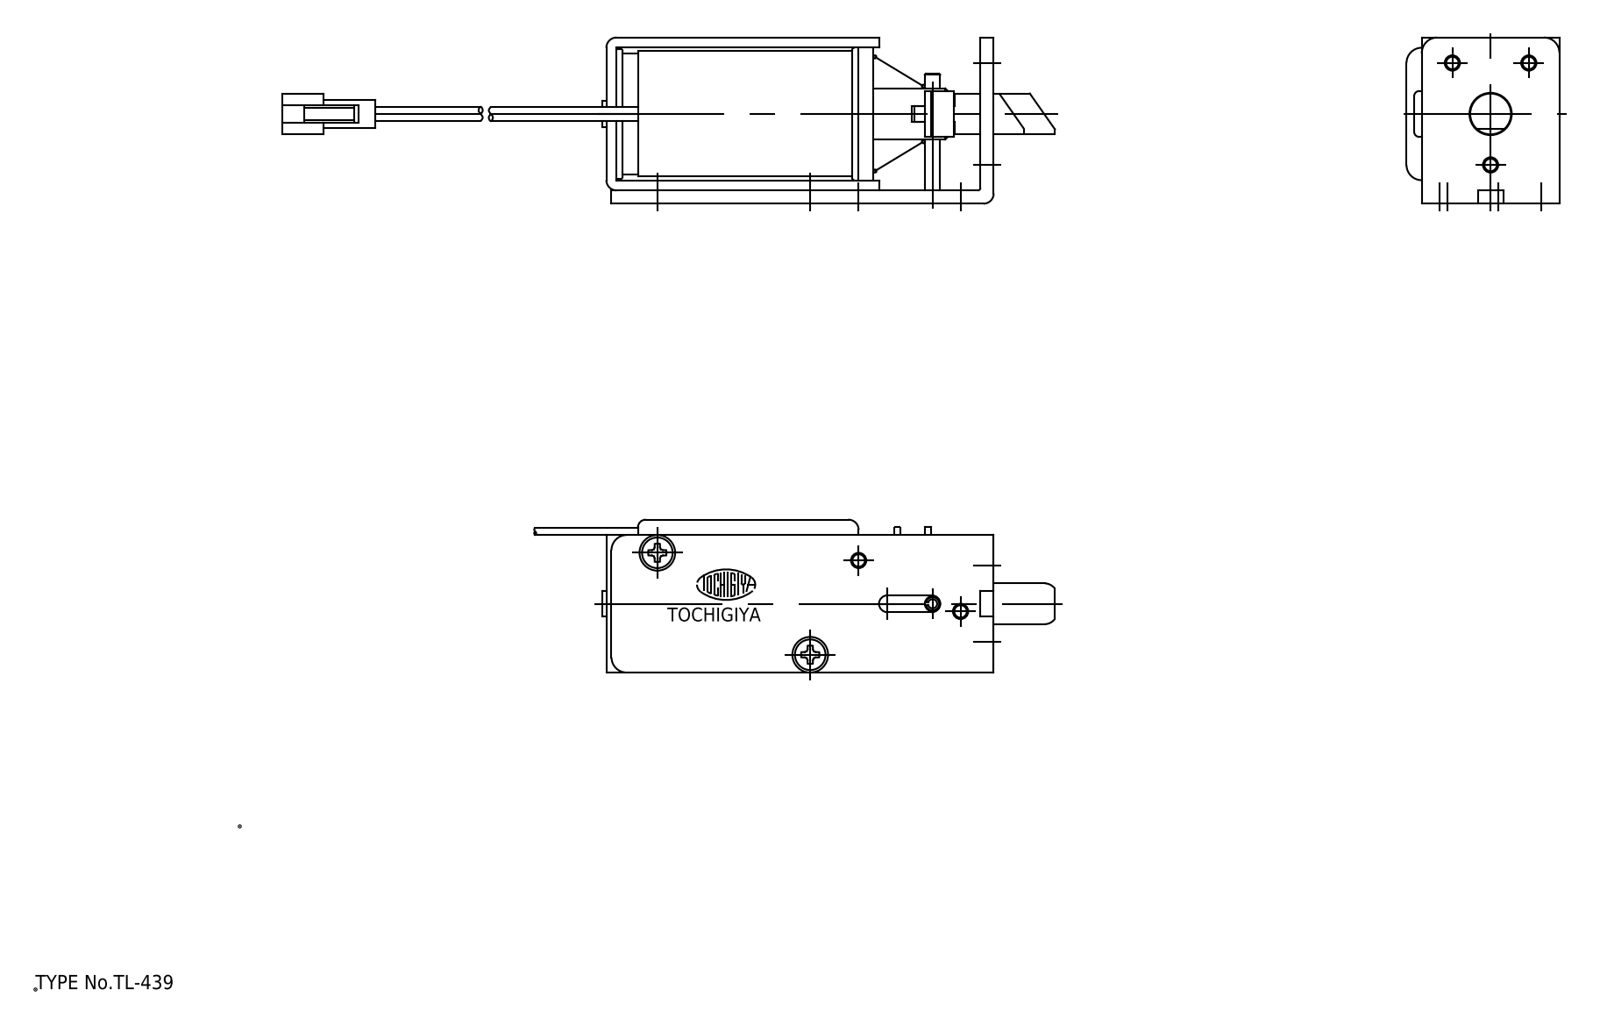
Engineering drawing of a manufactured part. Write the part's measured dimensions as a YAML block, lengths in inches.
part_name: "ベース; ラッチ; スプリング"
step_written_by: "spGate 18.9.1 (****-****-****-****) (AUTOMOTIVE_DESIGN)"
units: inches
bodies: {solids: 3, faces: 387, planar: 227, cylindrical: 106, other: 54}
overall_size: [5.809, 1.305, 1.283]
volume: 2.996
surface_area: 31.77
round_holes:
  - {diameter: 0.118, count: 9}
  - {diameter: 0.126, count: 2}
  - {diameter: 0.071, count: 1}
  - {diameter: 0.128, count: 1}
  - {diameter: 0.327, count: 1}
round_bosses_or_shafts:
  - {diameter: 0.236, count: 2}
  - {diameter: 0.055, count: 2}
  - {diameter: 0.929, count: 1}
  - {diameter: 0.394, count: 1}
  - {diameter: 0.315, count: 1}
  - {diameter: 0.197, count: 1}
  - {diameter: 0.118, count: 1}
partial_cylinders:
  - {radius: 0.02, count: 17}
  - {radius: 0.059, count: 8}
  - {radius: 0.039, count: 4}
  - {radius: 0.118, count: 4}
  - {radius: 0.079, count: 3}
  - {radius: 0.047, count: 2}
  - {radius: 0.065, count: 2}
  - {radius: 0.159, count: 1}
face_to_face_distances: [0.079, 1.102, 1.283, 0.102, 0.181, 1.205, 1.024, 1.181, 0.028, 0.996]
hole_center_spacings: [0.492, 0.787, 0.841, 1.024, 1.181, 1.42, 2.162, 0.224]
